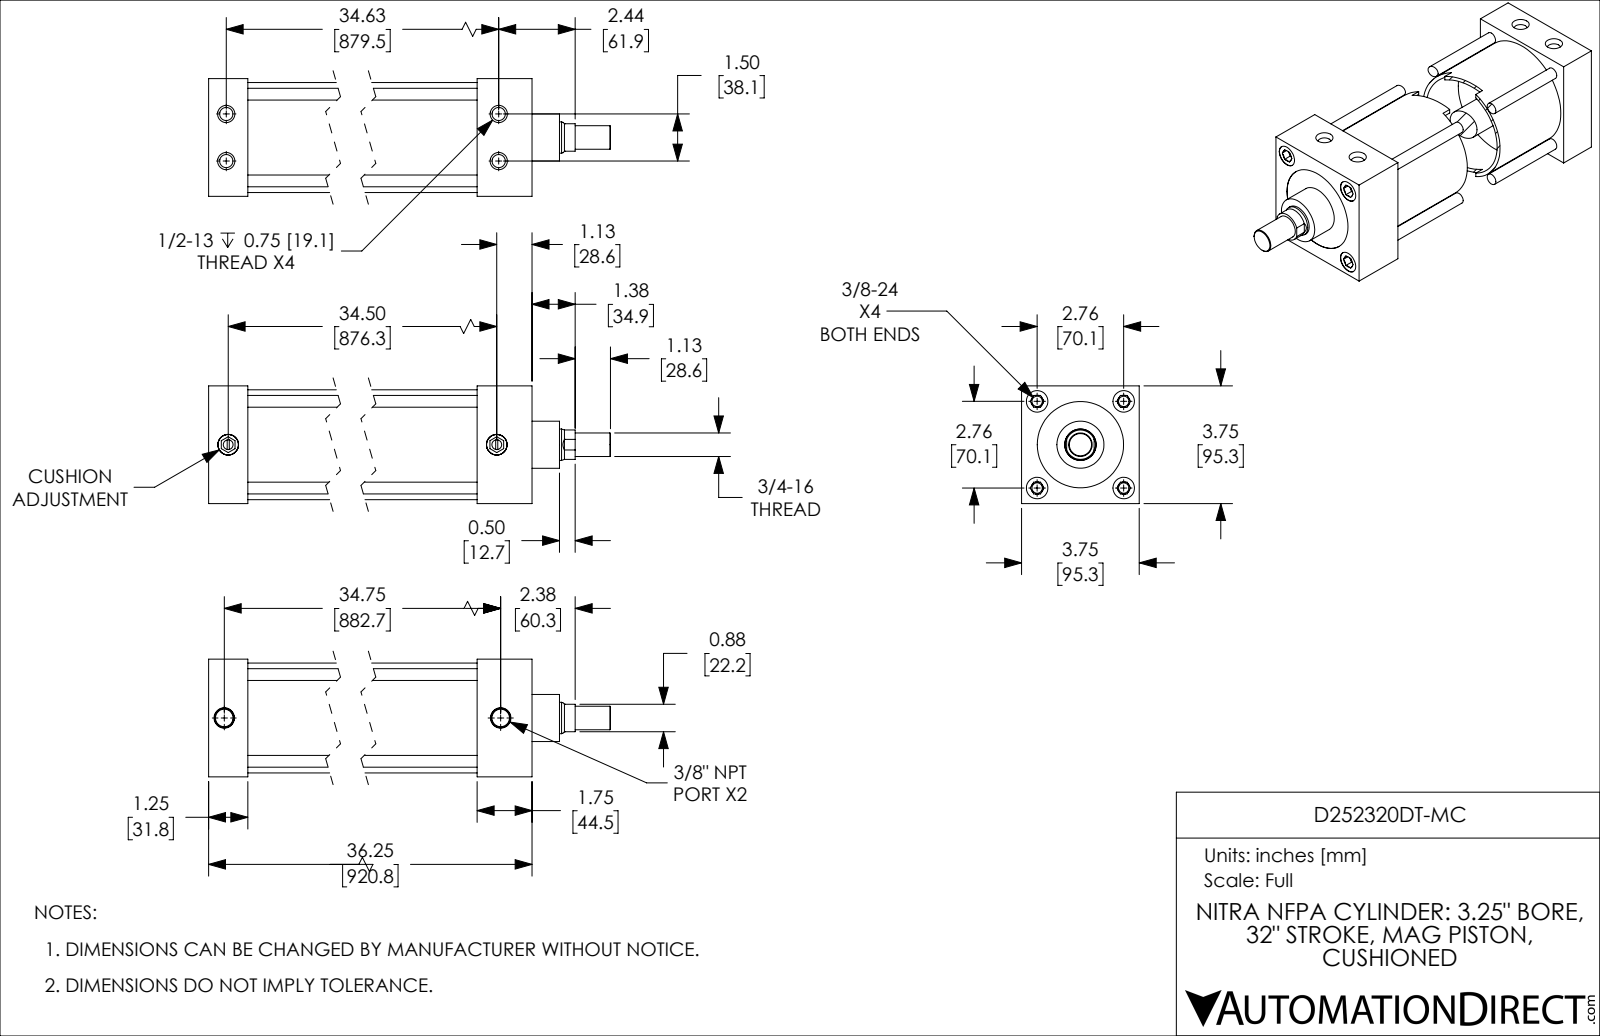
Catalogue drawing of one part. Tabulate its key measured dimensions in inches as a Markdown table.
| quantity | value |
| --- | --- |
| part name | D252320DT-MC_CUSHION; D252320DT-MC; D252320DT-MC_BODY; D252320DT-MC_PISTON_KK1 |
| STEP written by | SolidWorks 2019 (CONFIG_CONTROL_DESIGN) |
| units | inches |
| bodies | 4 solids, 246 faces (90 planar, 78 cylindrical, 78 other) |
| overall size | 38.75 × 3.75 × 3.75 |
| volume | 136.5 in³ |
| surface area | 1 136 in² |
| round holes (diameter × count) | 0.332 × 4, 0.422 × 4, 0.687 × 4, 0.312 × 2, 0.562 × 2, 0.656 × 2, 1.001 × 1, 2.75 × 1, 3.251 × 1 |
| round bosses / shafts (diameter × count) | 0.375 × 4, 0.657 × 2, 3.501 × 1, 3.249 × 1, 1.5 × 1, 0.999 × 1, 0.75 × 1 |
| partial cylindrical surfaces (radius × count) | 0.469 × 1 |
| main face-to-face distances | 1.25, 3.75, 34.5, 33.25, 2.5, 32, 36.25, 35, 33.75, 1.75 |
| hole center spacings | 0.753, 1.952, 2.76, 34.696, 1.5, 3.903, 34.625, 34.657 |
